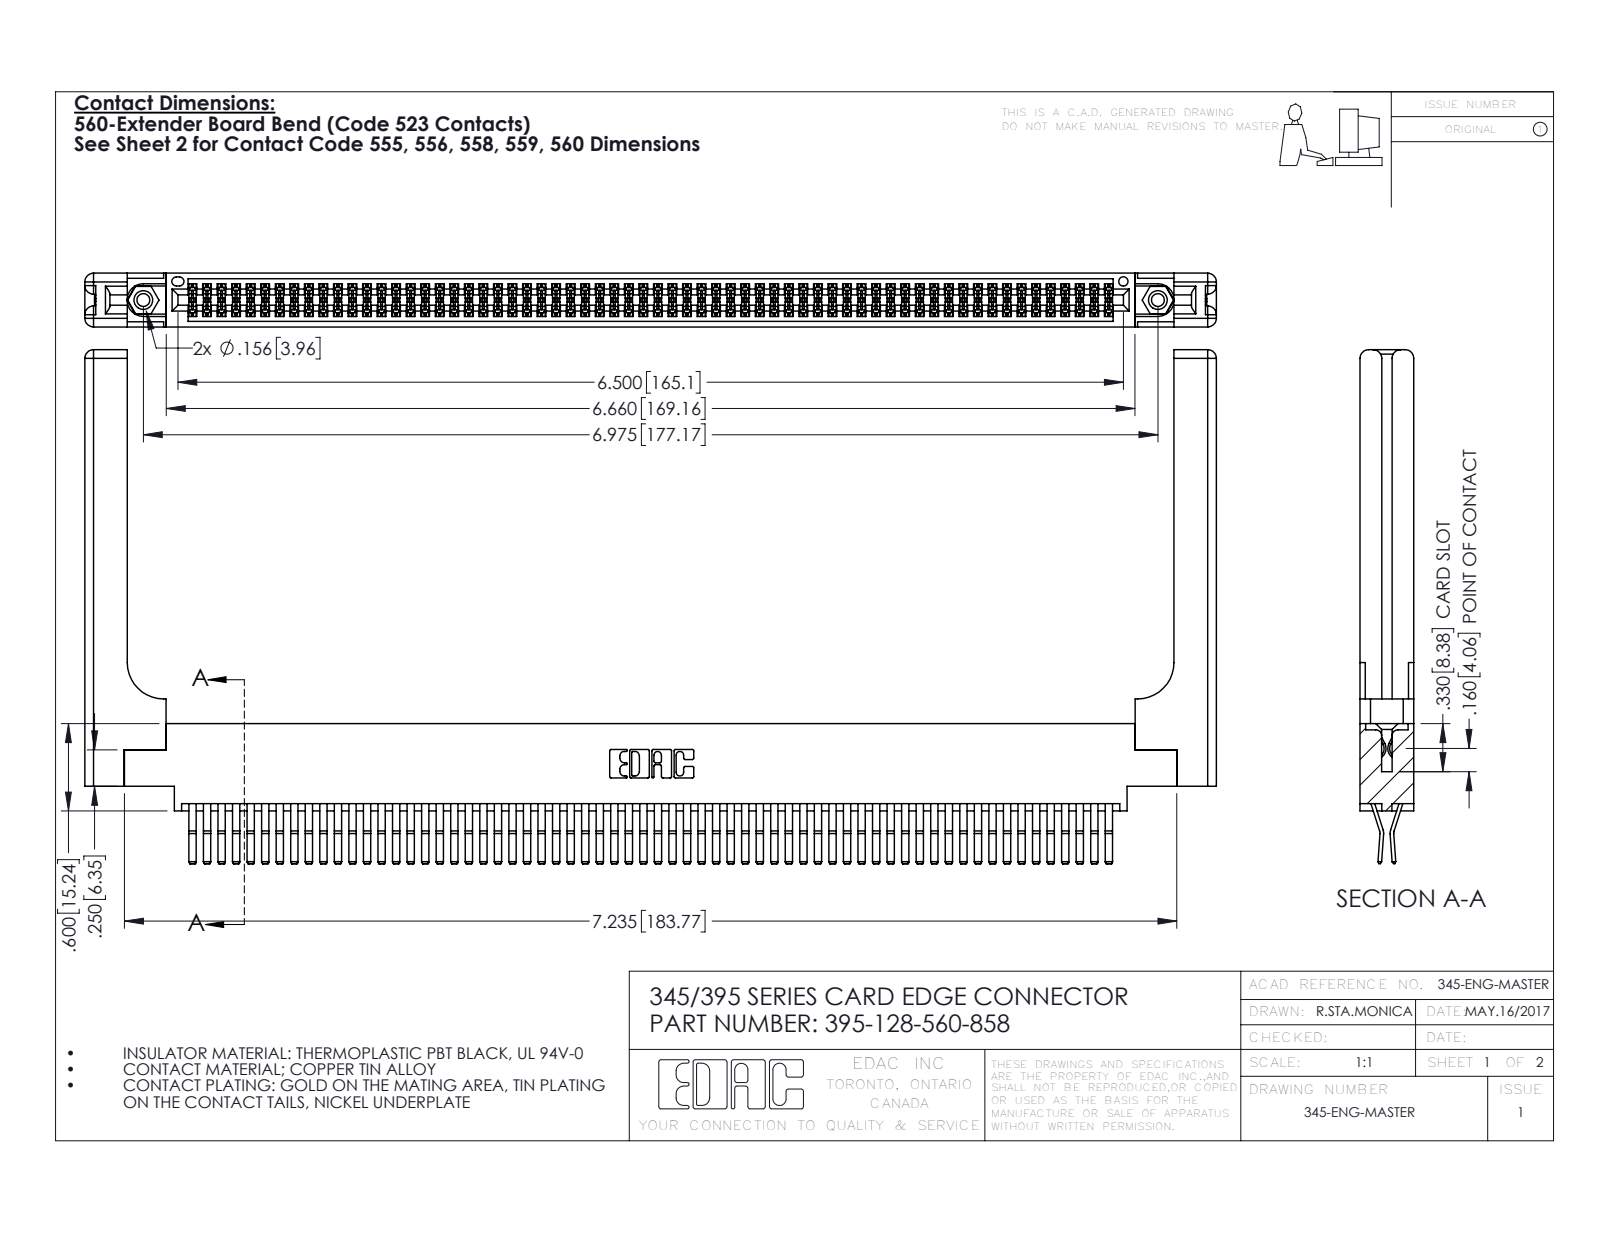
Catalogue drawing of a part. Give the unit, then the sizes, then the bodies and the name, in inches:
Units: inches
Overall size (bounding box): 7.779 × 3.532 × 0.37
Round holes (diameter × count): ⌀0.089 ×2, ⌀0.125 ×2, ⌀0.156 ×2, ⌀0.064 ×1
Round bosses / shafts (diameter × count): ⌀0.155 ×2
Partial cylindrical surfaces — rounded edges, fillets, slot ends (radius × count): R0.006 ×192, R0.01 ×22, R0.06 ×16, R0.007 ×6, R0.031 ×6, R0.026 ×3, R0.01 ×2, R0.014 ×2
Main face-to-face distances: 0.072, 0.298, 0.025, 0.37, 0.098, 0.272, 0.2, 0.225, 0.175, 0.148
Hole centre spacings: 0.27, 6.739, 6.975
Volume: 1.745 in³ · Surface area: 58.18 in²
Bodies: 133 solids, 7042 faces (4456 planar, 2526 cylindrical, 60 other)
Part name (STEP PRODUCT): 345 Part_0.170 Offset - 0.156 Dia-TH; 345-292-001_560 Tail; 395-128-560-858; 345-250-001_345-250-001-102 (+1 more)
STEP written by: SolidWorks 2016 (CONFIG_CONTROL_DESIGN)
